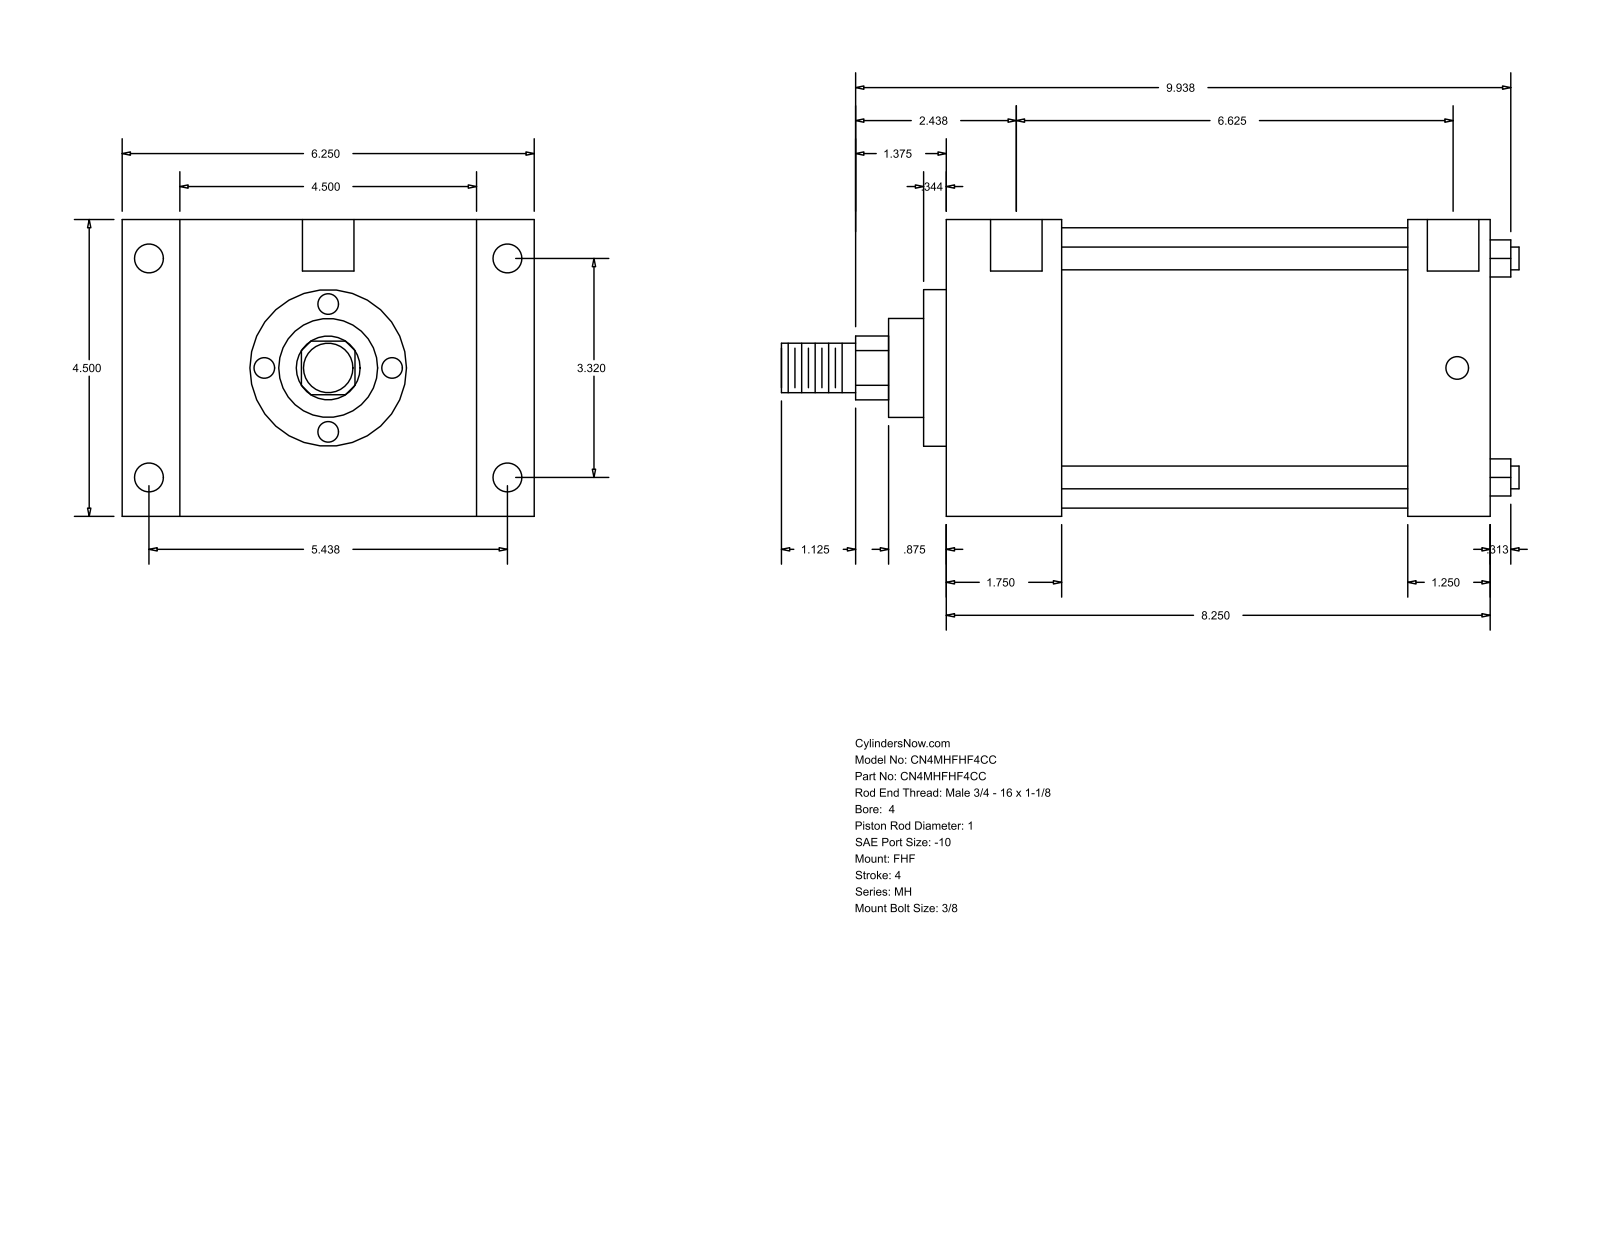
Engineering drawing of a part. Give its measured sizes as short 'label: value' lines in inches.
name: MH_FHF__0400_1
written by: GSSL Pune (CONFIG_CONTROL_DESIGN)
unit: in
bodies: 0 solids, 90 faces (61 planar, 29 cylindrical, 0 other)
size: 11.187 × 6.25 × 4.5
holes: 4× ⌀0.344, 4× ⌀0.438, 2× ⌀0.781
bosses: 4× ⌀0.345, 1× ⌀4.25, 1× ⌀2.375, 1× ⌀1.5, 1× ⌀1, 1× ⌀0.75
rounds: 1× R0.484
face distances: 4.5, 8.25, 1.75, 6.5, 0.875, 5.375, 6.25, 7, 5.25, 1.25
hole spacings: 3.32, 5.438, 6.371, 6.75, 0.062, 0.063, 6.625, 6.687
